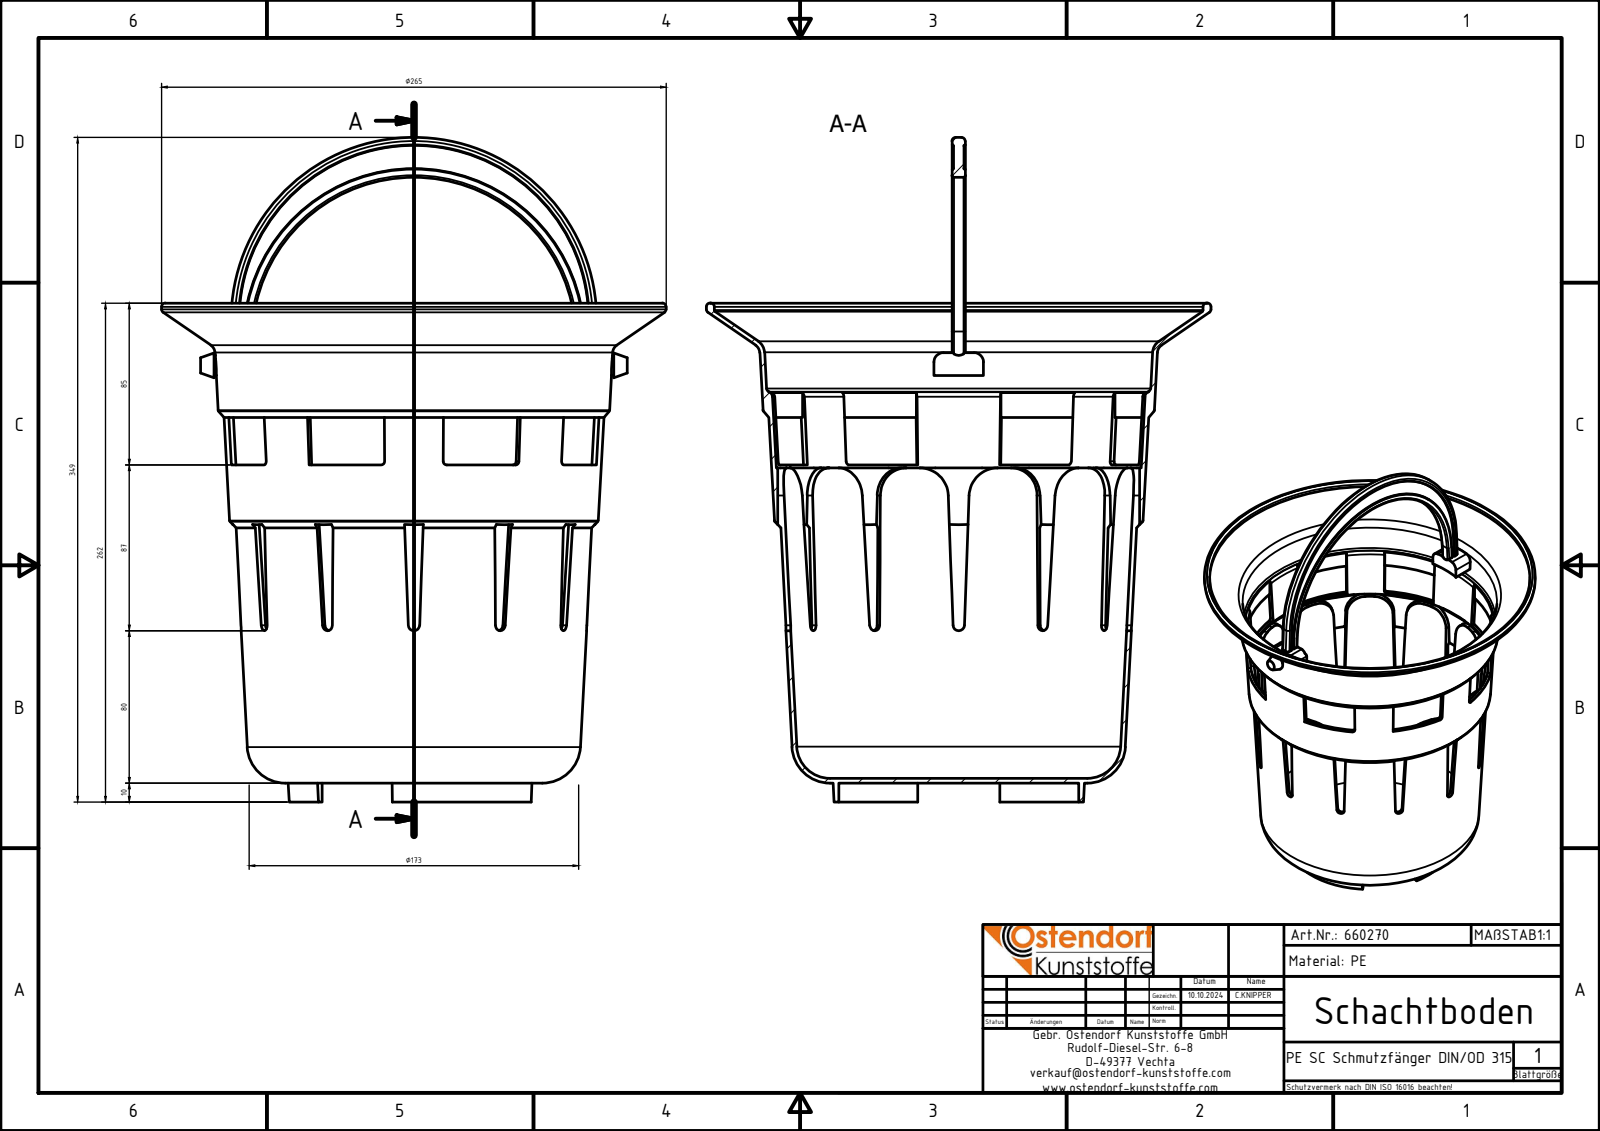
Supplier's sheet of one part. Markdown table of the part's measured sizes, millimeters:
| quantity | value |
| --- | --- |
| part name | 660270z |
| STEP written by | Autodesk Inventor 2024 (AUTOMOTIVE_DESIGN) |
| units | millimeters |
| bodies | 1 solid, 286 faces (158 planar, 90 cylindrical, 38 other) |
| overall size | 349 × 265 × 265 |
| volume | 521 561 mm³ |
| surface area | 367 197 mm² |
| round holes (diameter × count) | 256.6 × 1 |
| round bosses / shafts (diameter × count) | 265 × 1, 10.5 × 1 |
| partial cylindrical surfaces (radius × count) | 2 × 13, 15 × 12, 0.5 × 8, 3 × 6, 1 × 4, 5 × 3, 63 × 1, 85 × 1 |
| main face-to-face distances | 2.5, 0.75, 6.25, 190, 5.5, 7, 91.5, 92.25, 97.75, 98.5 |
